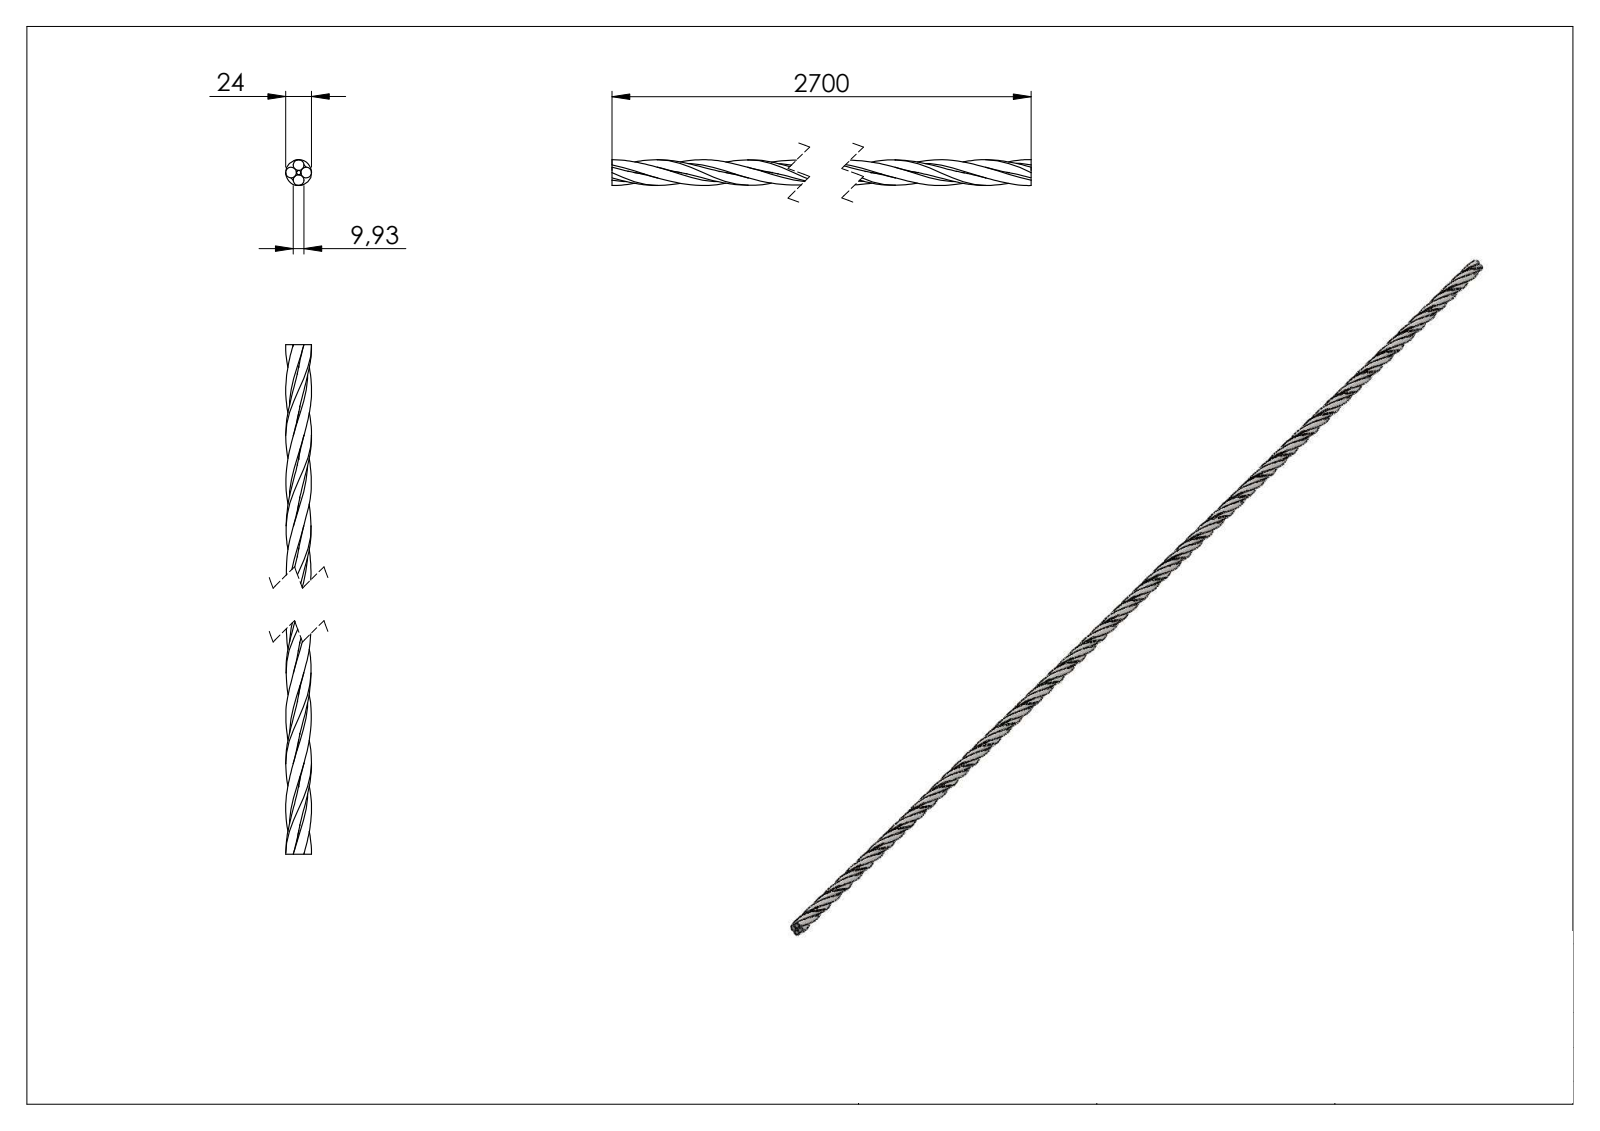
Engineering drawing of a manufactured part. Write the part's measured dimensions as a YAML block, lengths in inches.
part_name: "2024"
step_written_by: "SolidWorks 2015 (CONFIG_CONTROL_DESIGN)"
units: inches
bodies: {solids: 6, faces: 151, planar: 84, cylindrical: 0, other: 67}
overall_size: [106.299, 0.948, 0.946]
volume: 53.51
surface_area: 521.8
face_to_face_distances: [106.299, 0.02, 106.28, 0.07, 0.03, 0.039, 0.106, 0.027, 0.017, 0.109]
